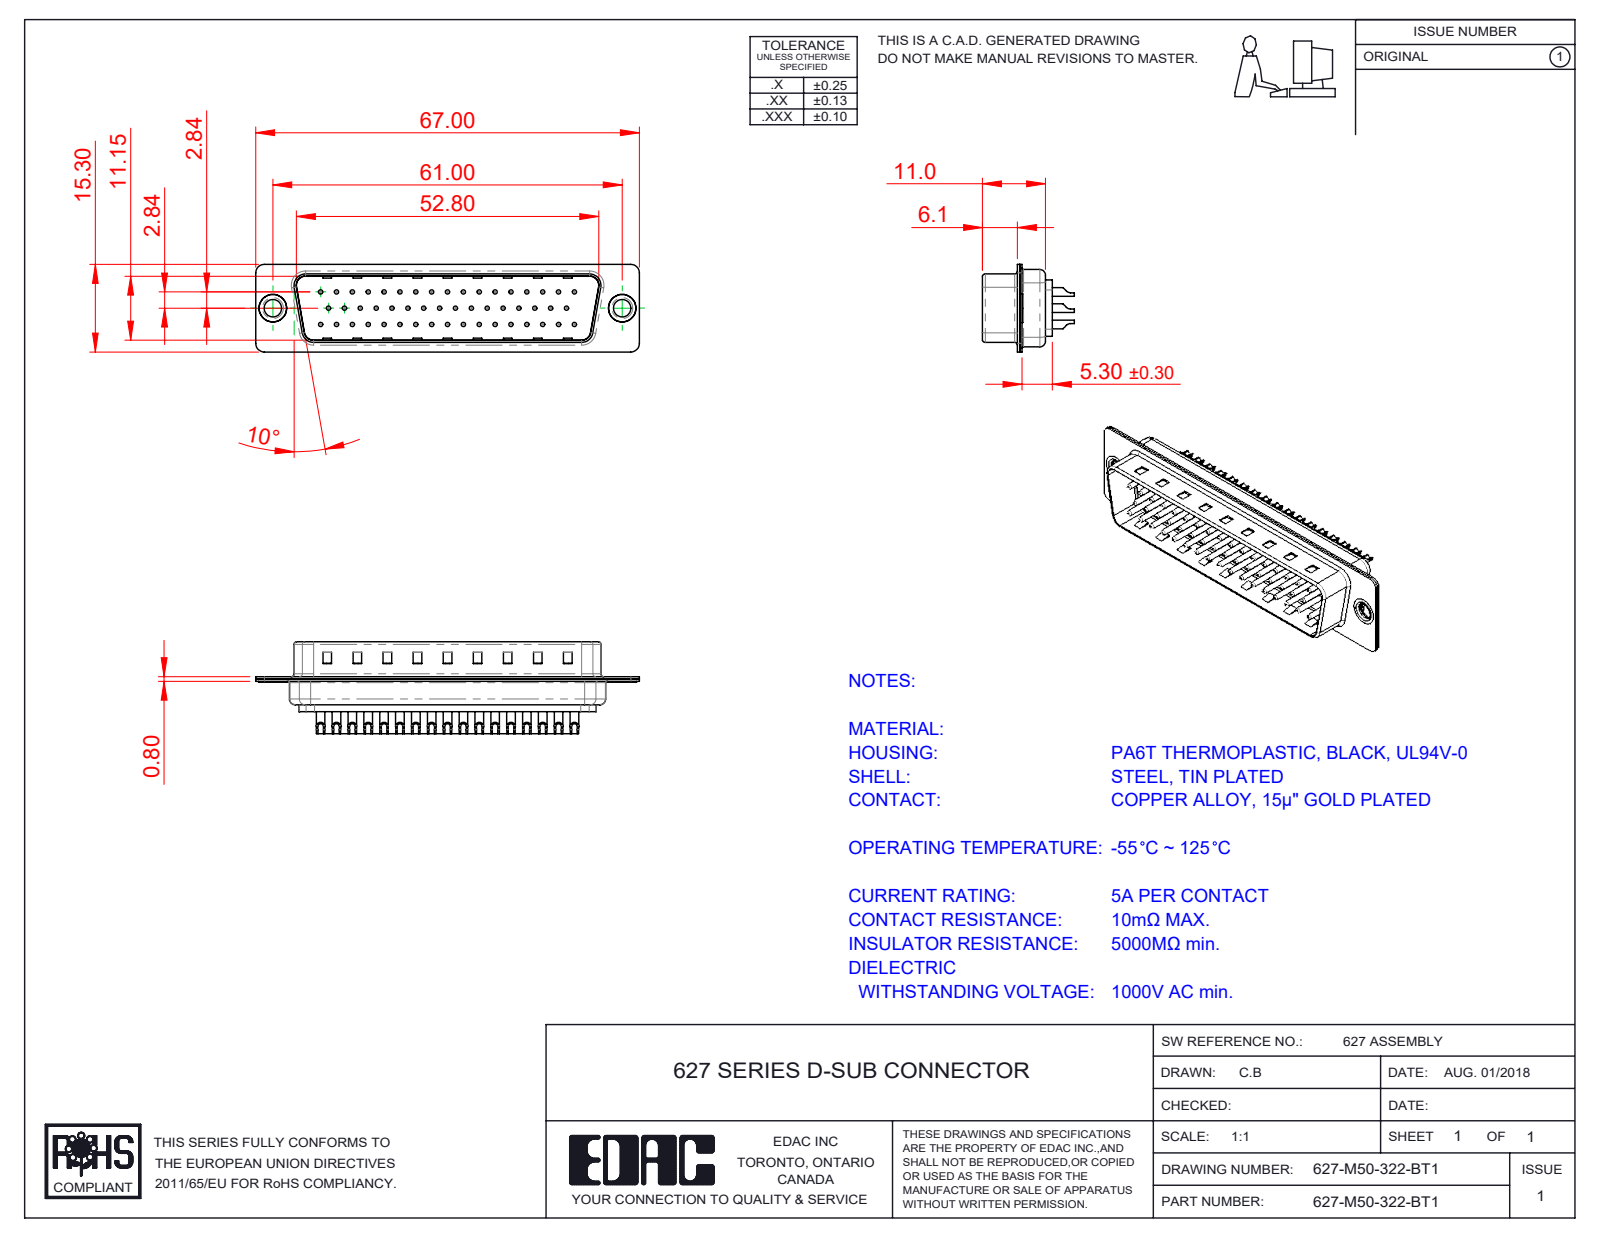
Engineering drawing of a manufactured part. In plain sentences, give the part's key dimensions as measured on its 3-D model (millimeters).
The part is named "627M Contact Row 2_22L; 627M Contact Row 3_22; 627-M50-322-BT1; 627M Shell Rear_50 Contacts (+4 more)". Its 3-D file was written by "SolidWorks 2020 (CONFIG_CONTROL_DESIGN)". It is 55 solids with 2236 faces: 653 planar, 925 cylindrical and 658 other. Overall it measures 67 by 16.05 by 15.3 millimeters. Its volume is 4 561 cubic millimeters and its surface area 11 022 square millimeters. Round holes: 50 of diameter 0.75, 50 of diameter 1, 50 of diameter 1.6, 50 of diameter 2, 2 of diameter 3.05, 2 of diameter 4, 2 of diameter 4.8. Round bosses or shafts: 50 of diameter 1.5, 2 of diameter 5, 2 of diameter 4.9, 2 of diameter 3.55. Partial cylindrical surfaces (rounded edges, fillets, slot ends): 16 of radius 1.5, 12 of radius 2, 8 of radius 0.5, 8 of radius 1.6, 7 of radius 1, 4 of radius 0.25, 4 of radius 0.6, 4 of radius 0.65. The main face-to-face distances are 0.4, 11.55, 5.7, 6.1, 0.78, 0.77, 12.33, 12.32, 13.1, 5.3. The hole center spacings are 3.16, 2.77, 5.54, 8.31, 11.08, 13.85, 16.62, 5.03.
